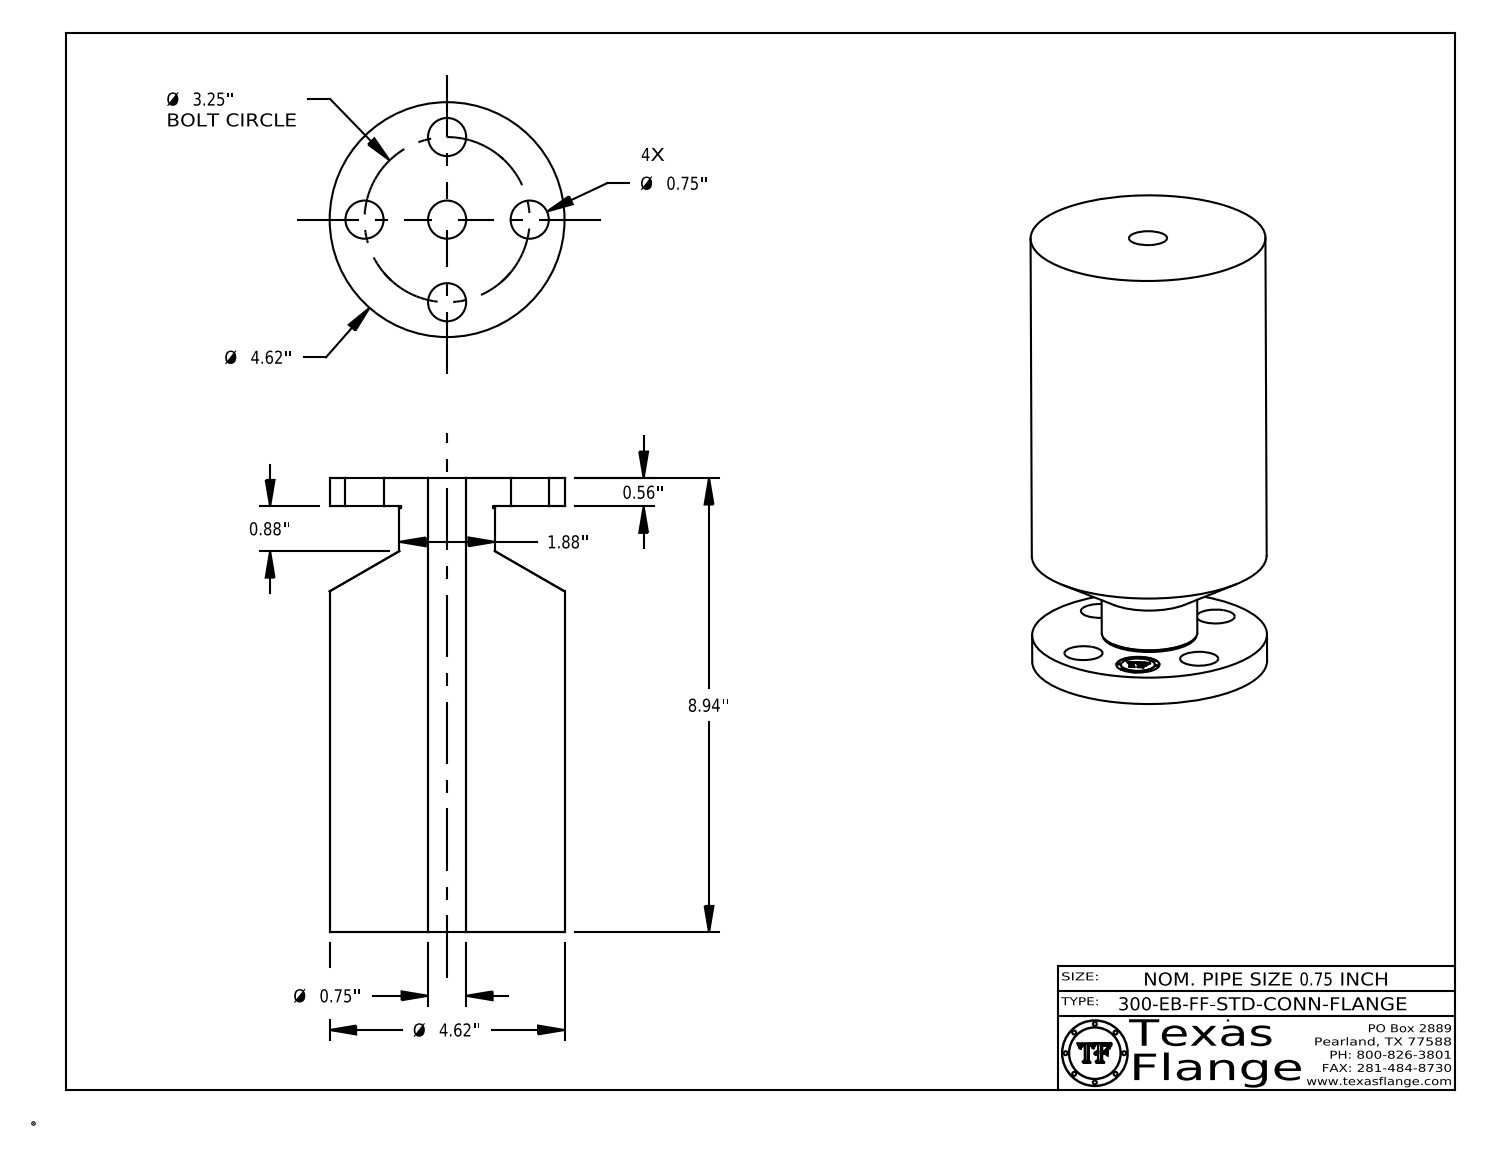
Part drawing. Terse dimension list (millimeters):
name: 0.75-300-EB-FF-STD-CONN-FLANGE
written by: CATIA V5 STEP AP214 (AUTOMOTIVE_DESIGN)
unit: mm
bodies: 1 solid, 410 faces (368 planar, 36 cylindrical, 6 other)
size: 227 × 117.3 × 117.3
volume: 2 070 000 mm³; area: 126 800 mm²
holes: 5× ⌀19.1, 1× ⌀21.6
bosses: 8× ⌀1.3, 1× ⌀117.3, 1× ⌀47.8, 1× ⌀17
face distances: 227, 14.1, 212.9, 14, 213, 6.5, 6.3, 0.4, 1.2, 4.2
hole spacings: 41.3, 58.4, 31.6, 76.3, 82.6
